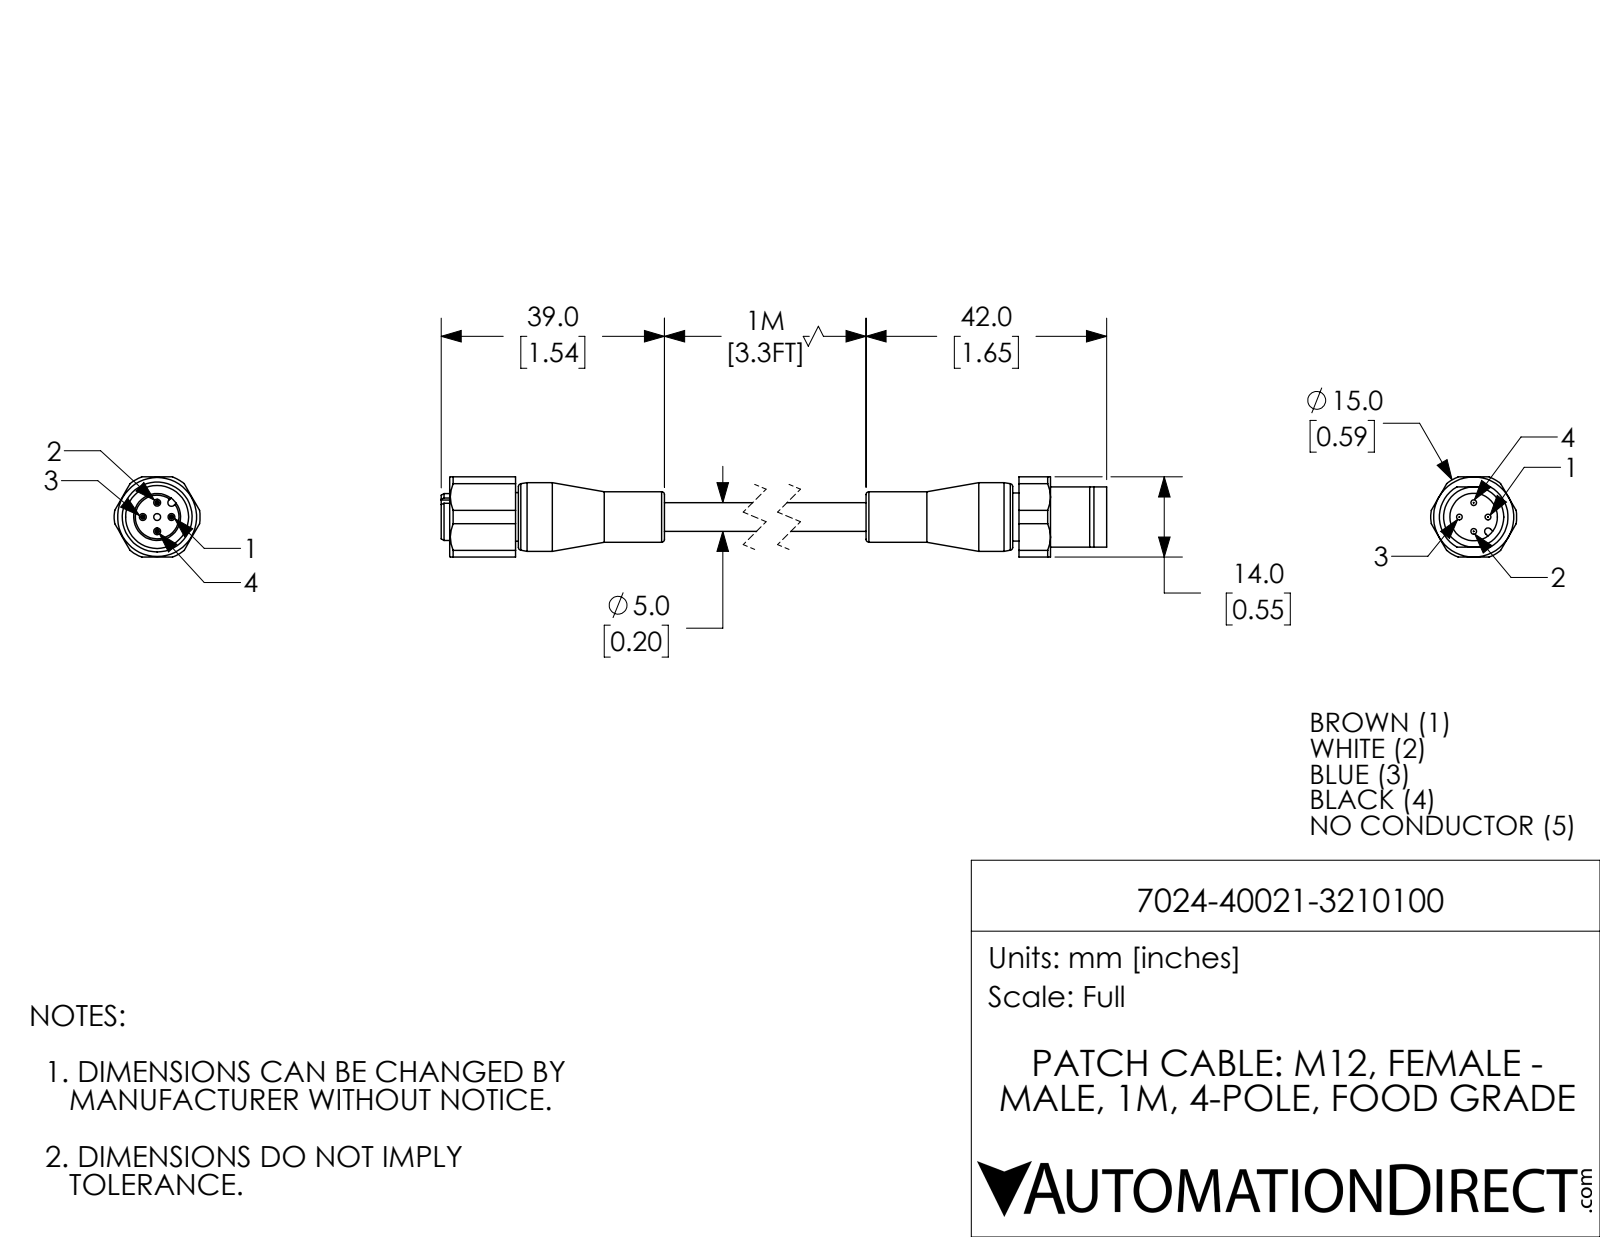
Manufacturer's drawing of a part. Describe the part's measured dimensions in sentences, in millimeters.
The part is named "7024-40021-3210100; 7024-40021-3210100_MALE; 7024-40021-3210100_FEMALE". Its 3-D file was written by "SolidWorks 2018 (AUTOMOTIVE_DESIGN)". It is 2 solids with 144 faces: 43 planar, 60 cylindrical and 41 other. Overall it measures 131.2 by 15 by 14 millimeters. Its volume is 8 050 cubic millimeters and its surface area 5 071 square millimeters. Round holes: 5 of diameter 1.2, 1 of diameter 8.3, 1 of diameter 11. Round bosses or shafts: 4 of diameter 1, 1 of diameter 12, 1 of diameter 10.5, 1 of diameter 8.8, 1 of diameter 8.5, 1 of diameter 8.4, 1 of diameter 8.2, 1 of diameter 5. Partial cylindrical surfaces (rounded edges, fillets, slot ends): 1 of radius 0.6, 1 of radius 0.7, 1 of radius 7.5. The main face-to-face distances are 14, 102.9, 1.8, 12.2, 113.3, 7.5, 5.5, 109.3, 6.4, 108.4. The hole center spacings are 2.5, 3.5, 5.
